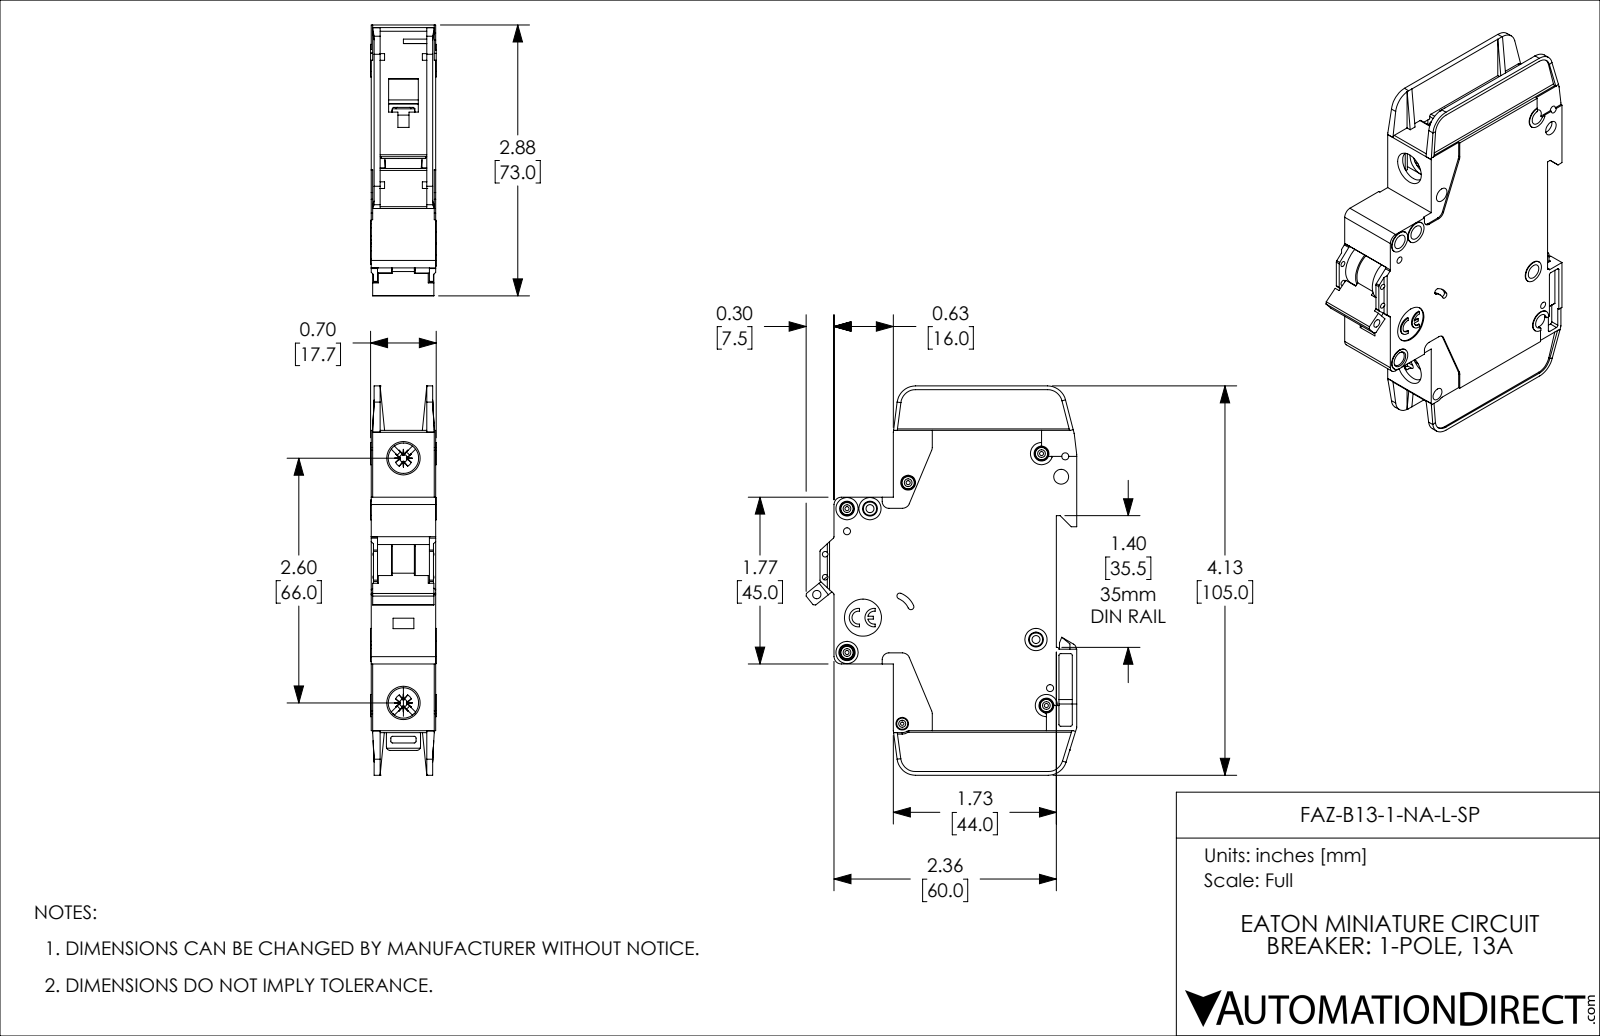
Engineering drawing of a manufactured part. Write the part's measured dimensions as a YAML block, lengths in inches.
part_name: "FAZ-B13-1-NA-L-SP"
step_written_by: "SolidWorks 2019 (AUTOMOTIVE_DESIGN)"
units: inches
bodies: {solids: 1, faces: 1127, planar: 671, cylindrical: 357, other: 99}
overall_size: [4.134, 2.876, 0.697]
volume: 4.682
surface_area: 41.01
round_holes:
  - {diameter: 0.157, count: 8}
  - {diameter: 0.043, count: 5}
  - {diameter: 0.075, count: 4}
  - {diameter: 0.059, count: 2}
  - {diameter: 0.085, count: 2}
  - {diameter: 0.323, count: 2}
  - {diameter: 0.035, count: 1}
  - {diameter: 0.089, count: 1}
  - {diameter: 0.098, count: 1}
  - {diameter: 0.134, count: 1}
  - {diameter: 0.394, count: 1}
round_bosses_or_shafts:
  - {diameter: 0.13, count: 5}
  - {diameter: 0.236, count: 4}
  - {diameter: 0.118, count: 2}
  - {diameter: 0.098, count: 1}
partial_cylinders:
  - {radius: 0.02, count: 42}
  - {radius: 0.016, count: 10}
  - {radius: 0.039, count: 10}
  - {radius: 0.079, count: 8}
  - {radius: 0.197, count: 5}
  - {radius: 0.008, count: 4}
  - {radius: 0.026, count: 4}
  - {radius: 0.043, count: 4}
face_to_face_distances: [0.047, 0.685, 0.591, 0.638, 0.094, 0.543, 0.016, 0.031, 0.496, 0.575]
hole_center_spacings: [0.244, 0.537, 0.87, 0.189, 0.199, 0.204, 0.221, 0.24]
